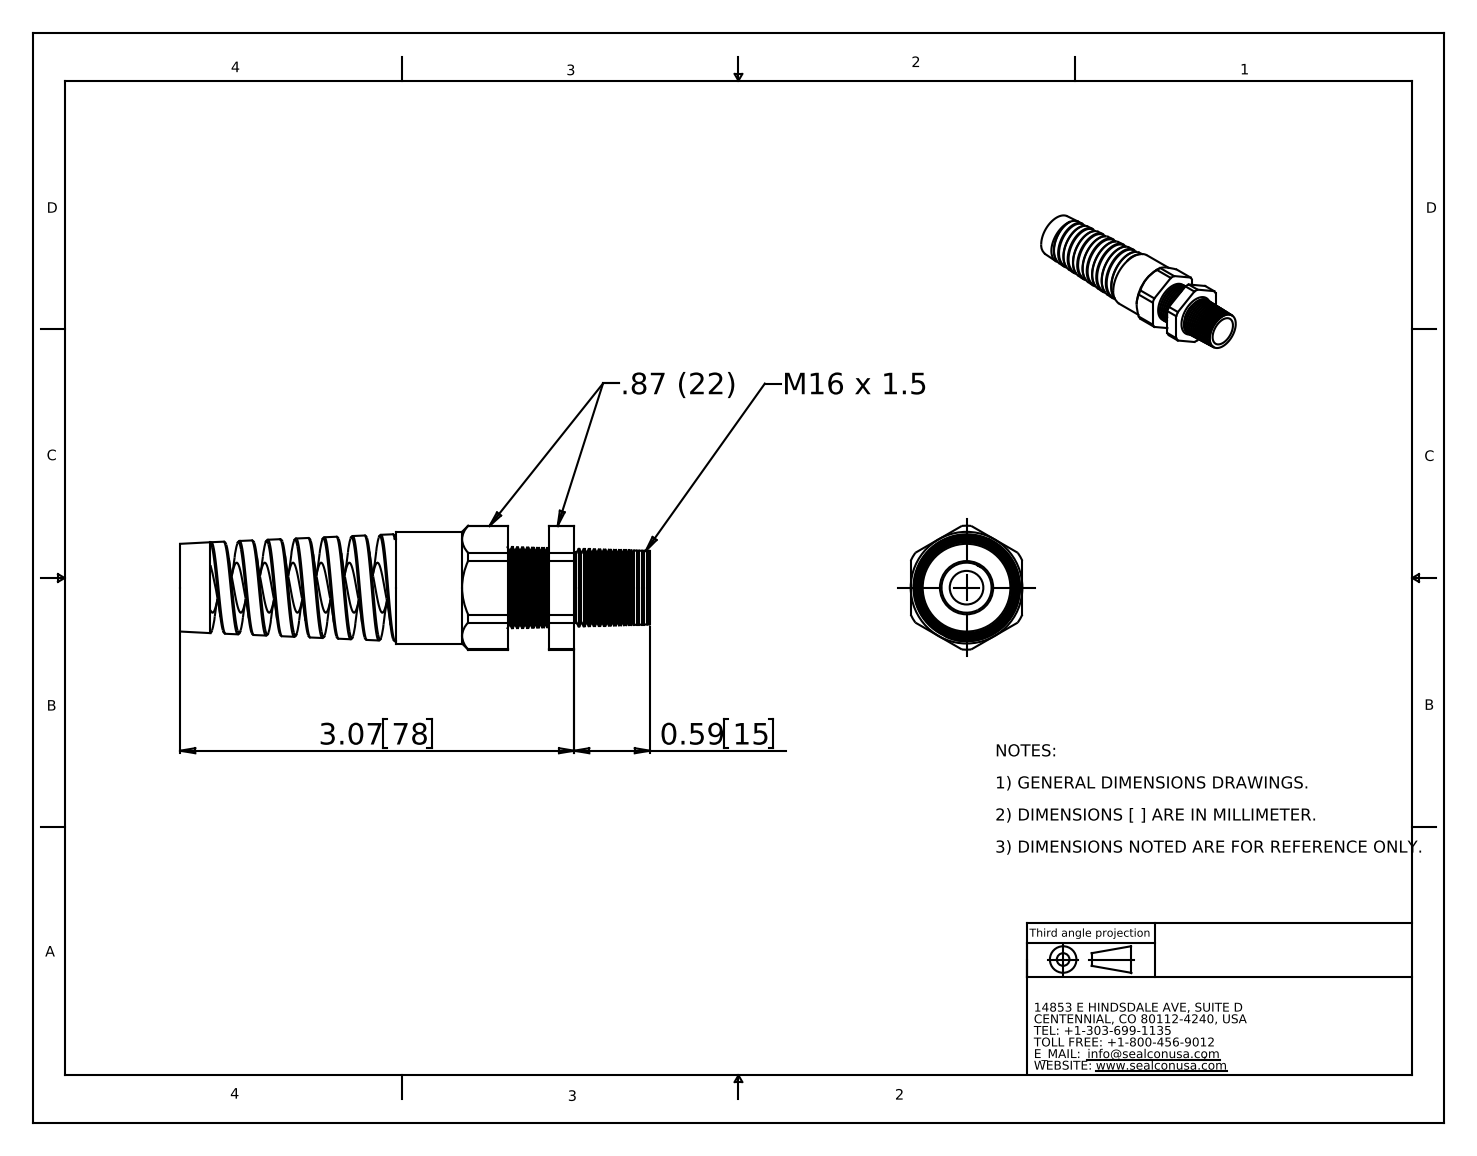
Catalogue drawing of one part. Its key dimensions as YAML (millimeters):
part_name: "CF17DR-GY"
step_written_by: "SolidWorks 2008 (CONFIG_CONTROL_DESIGN)"
units: millimeters
bodies: {solids: 2, faces: 239, planar: 25, cylindrical: 39, other: 175}
overall_size: [93, 24.5, 22.1]
volume: 16670
surface_area: 12450
round_holes:
  - {diameter: 6.7, count: 1}
  - {diameter: 9.9, count: 1}
  - {diameter: 10.5, count: 1}
round_bosses_or_shafts:
  - {diameter: 22.1, count: 1}
  - {diameter: 16.1, count: 1}
partial_cylinders:
  - {radius: 12.3, count: 1}
face_to_face_distances: [22.1, 8.2, 13.2, 5, 9, 17.2, 22.2, 55.8, 64.8, 73]
